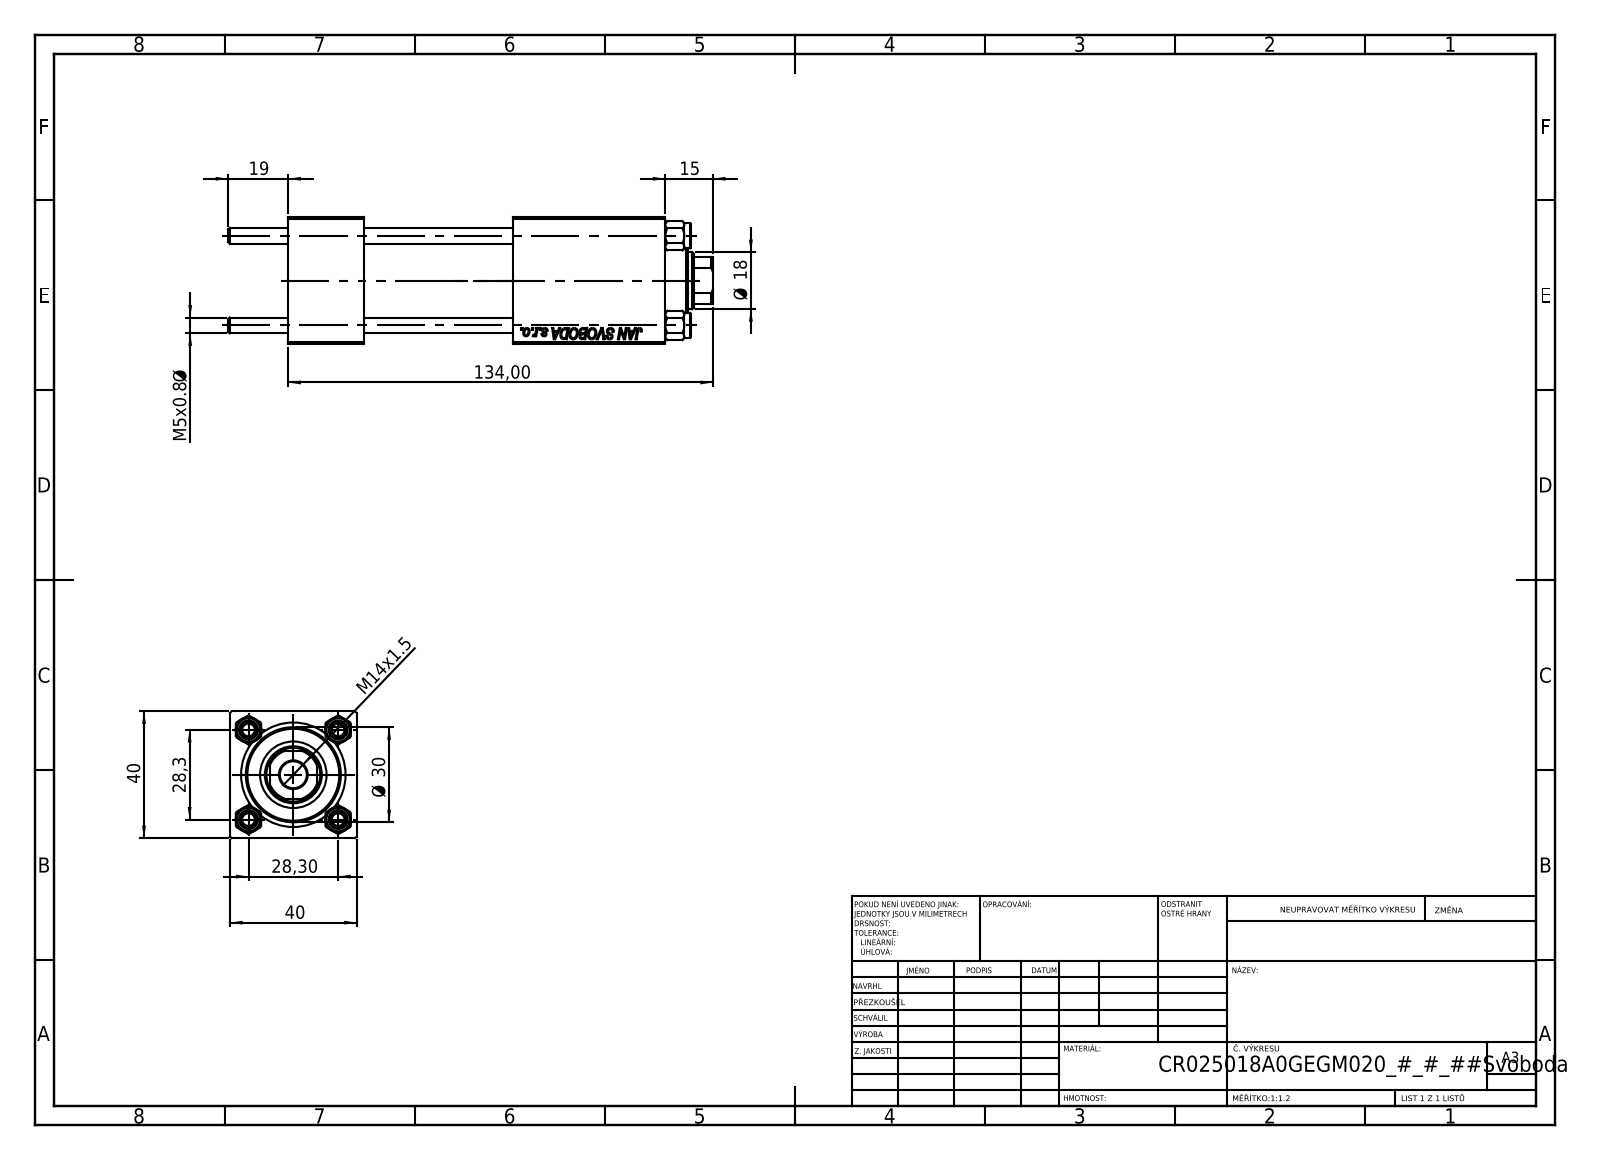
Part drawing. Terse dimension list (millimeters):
name: V215CR_BODY_A; NUT_M5; V215CR_VCP; CR025_012_A_0_G_A_G_M_020_+#_##_TYCINKA (+1 more)
written by: SolidWorks 2019 (CONFIG_CONTROL_DESIGN)
unit: mm
bodies: 11 solids, 1129 faces (516 planar, 77 cylindrical, 536 other)
size: 153 × 40 × 40
volume: 152 396 mm³; area: 61 142 mm²
holes: 4× ⌀5, 3× ⌀20, 2× ⌀7, 1× ⌀8.5, 1× ⌀13, 1× ⌀13.16, 1× ⌀18, 1× ⌀21, 1× ⌀25, 1× ⌀30
bosses: 4× ⌀8, 1× ⌀31
rounds: 1× R8.5
face distances: 40, 24, 71, 47, 90.3, 66.3, 19.3, 119, 95, 48
hole spacings: 20.01, 28.3, 40.02, 72
